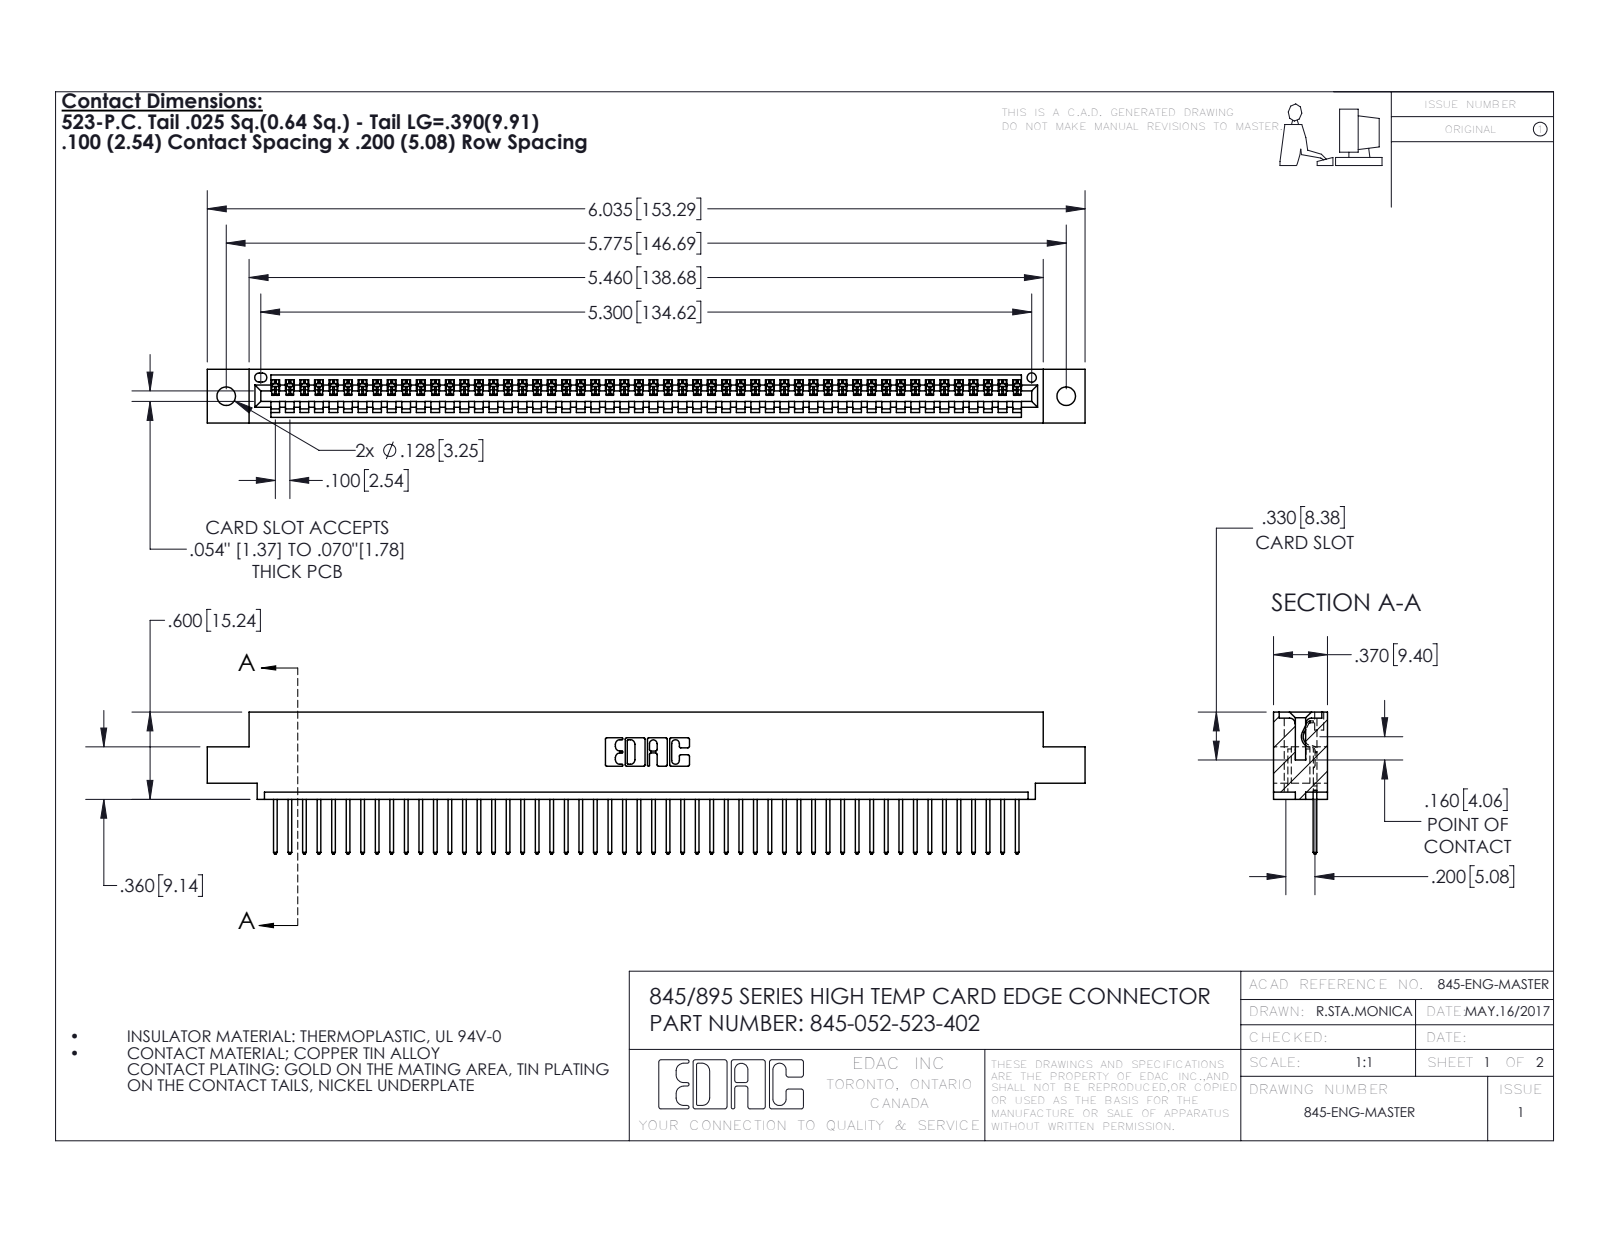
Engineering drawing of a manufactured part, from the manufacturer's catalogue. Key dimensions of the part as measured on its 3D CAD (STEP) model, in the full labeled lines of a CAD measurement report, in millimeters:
Part name (STEP PRODUCT): 345-052-523-402; 345-292-001_345-293-123; 345 Part_0.110 Offset - 0.128 Dia
STEP written by: SolidWorks 2016 (CONFIG_CONTROL_DESIGN)
Units: millimetres
Bodies: 53 solids, 3146 faces (2164 planar, 982 cylindrical, 0 other)
Overall size (bounding box): 153.3 × 24.8 × 9.4
Volume: 14 500 mm³ · Surface area: 19 290 mm²
Round holes (diameter × count): ⌀3.3 ×2, ⌀1.6 ×1
Partial cylindrical surfaces — rounded edges, fillets, slot ends (radius × count): R0.2 ×104, R0.3 ×104, R0.3 ×22, R0.2 ×6, R0.8 ×6, R0.7 ×3, R0.8 ×2, R1 ×2
Main face-to-face distances: 7.6, 1.8, 9.4, 2.5, 6.9, 0.6, 5.1, 5.7, 3.8, 1.8
Hole centre spacings: 6.9, 140.7, 146.7
